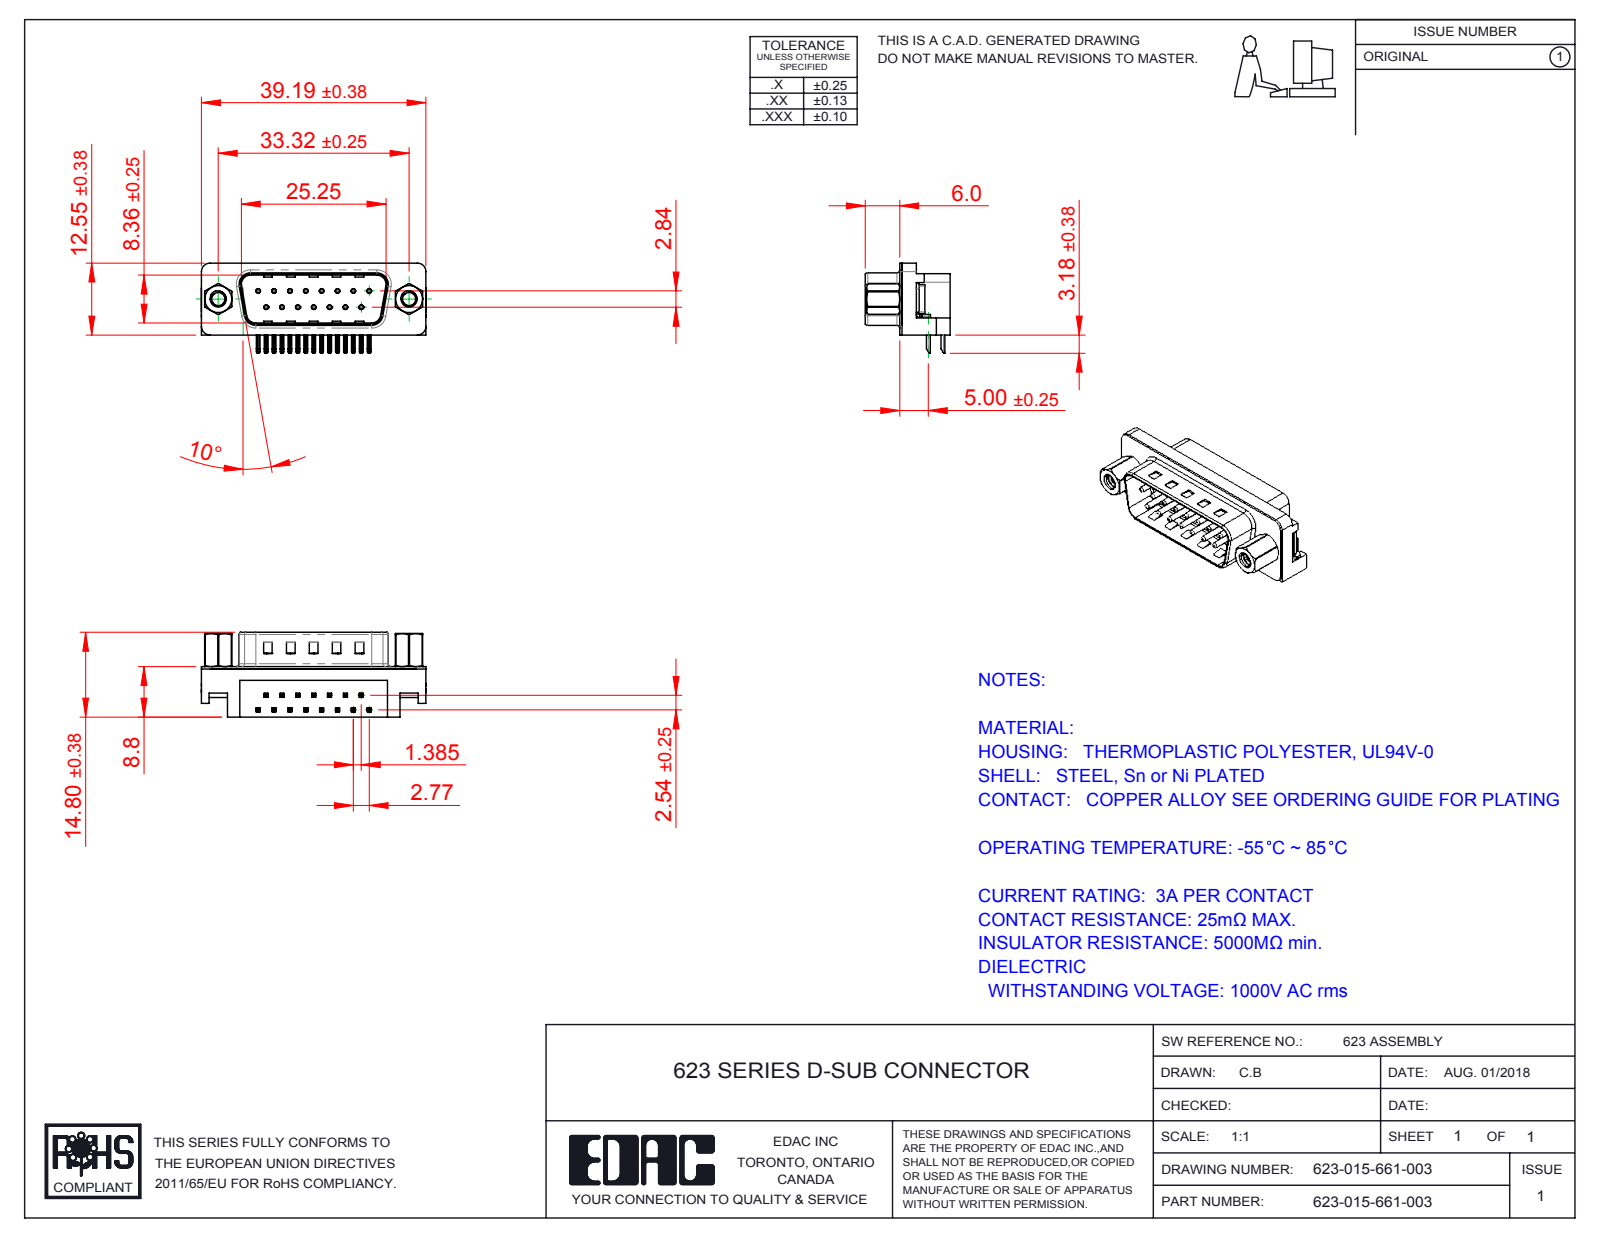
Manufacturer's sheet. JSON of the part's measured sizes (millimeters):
{"part_name": "623 Contact Top; 623 Contact Bottom; 623 Non Board Mount; 623 4-40 Hex Standoff 5 (+4 more)", "step_written_by": "SolidWorks 2016 (CONFIG_CONTROL_DESIGN)", "units": "millimeters", "bodies": {"solids": 23, "faces": 1591, "planar": 915, "cylindrical": 503, "other": 173}, "overall_size": [39.22, 15.73, 14.8], "volume_mm3": 3527, "surface_area_mm2": 5355, "round_holes": [[0.35, 15], [0.8, 15], [2.26, 2], [2.29, 2], [4, 2], [4.8, 2], [5, 2]], "round_bosses_or_shafts": [[0.75, 15], [4.9, 2], [4.75, 2], [3.9, 2], [2.79, 2]], "partial_cylinders_radius": [[0.25, 68], [0.12, 30], [1, 16], [0.5, 9], [1.5, 6], [0.9, 4], [1.6, 4], [2, 4]], "face_to_face_distances": [0.4, 8.4, 8.8, 2.1, 1.7, 10.46, 10.86, 8.76, 5.9, 2.9], "hole_center_spacings": [3.16, 2.77, 5.54, 8.31, 11.08, 5.03, 5.04, 7.48]}
